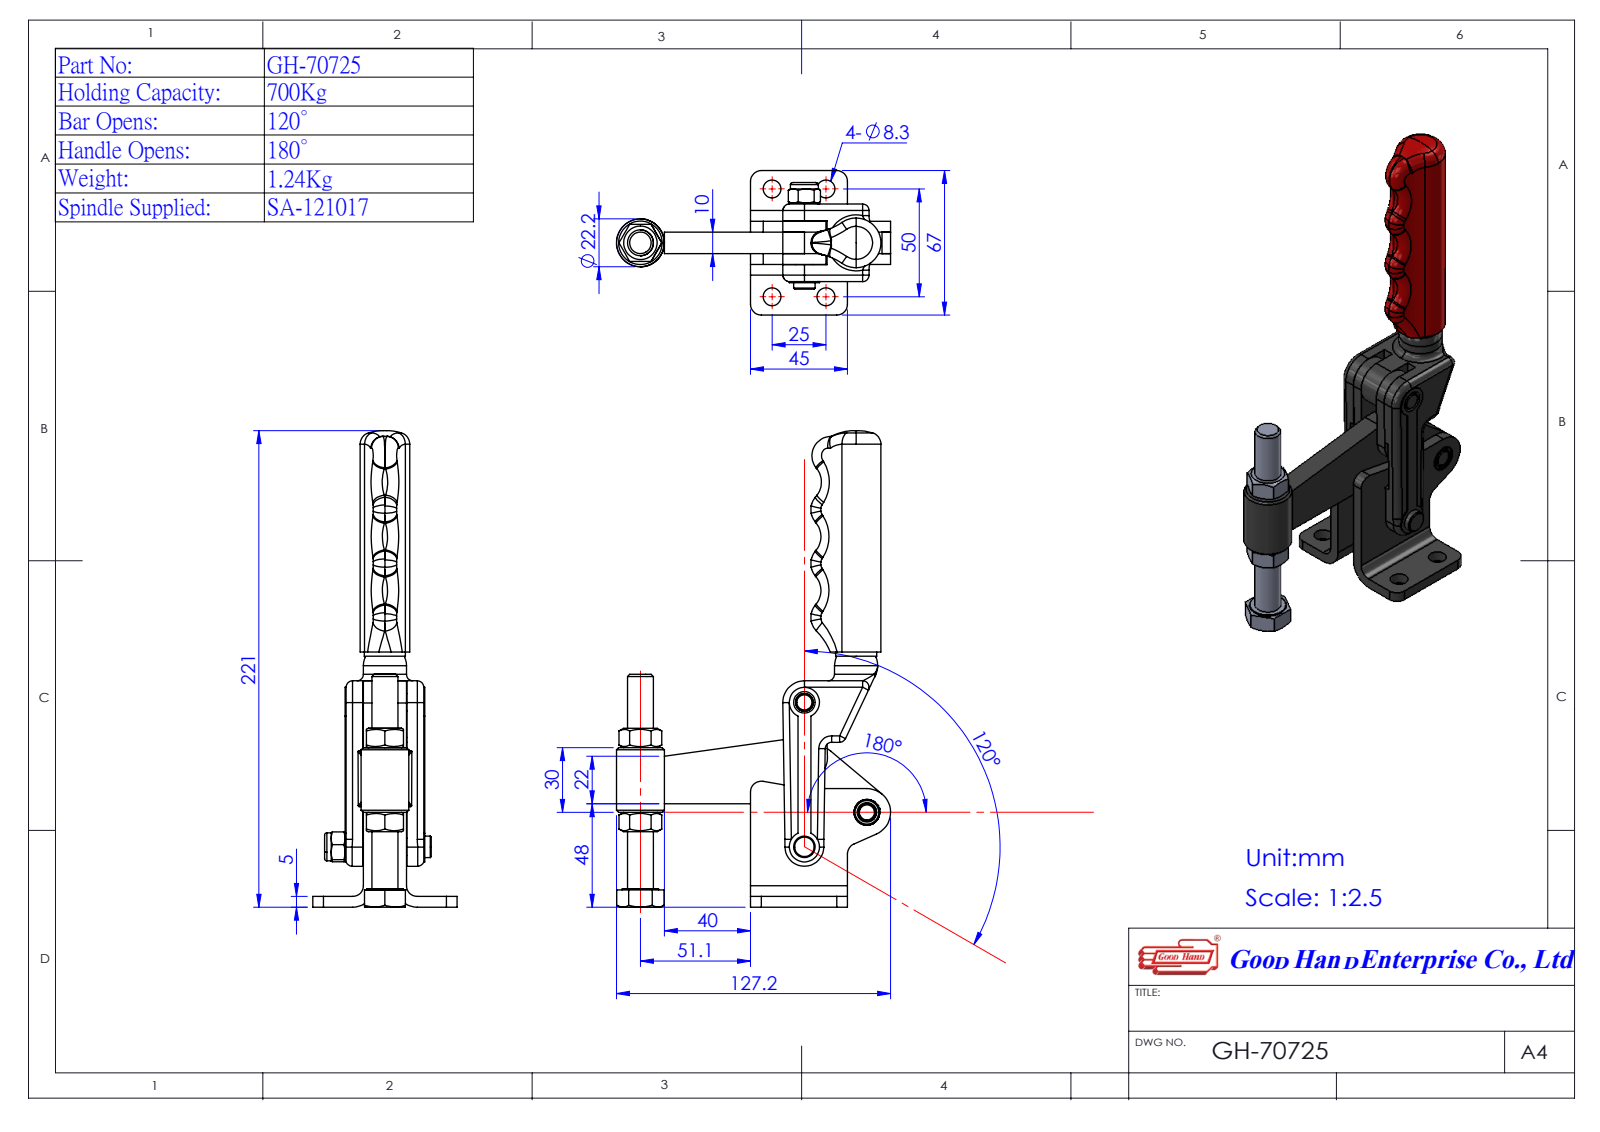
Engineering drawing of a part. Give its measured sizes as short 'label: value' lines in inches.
name: Group1^GH-70725(簡化)-1; Group5^GH-70725(簡化)-1; Group4^GH-70725(簡化)-1; GH-70725(簡化)-1 (+2 more)
written by: SolidWorks 2016 (AUTOMOTIVE_DESIGN)
unit: in
bodies: 6 solids, 362 faces (110 planar, 128 cylindrical, 124 other)
size: 8.702 × 5.008 × 2.638
volume: 12.06 in³; area: 100.7 in²
holes: 4× ⌀0.236, 4× ⌀0.327
bosses: 2× ⌀0.551, 1× ⌀0.874, 1× ⌀0.787, 1× ⌀0.75, 1× ⌀0.709, 1× ⌀0.472, 1× ⌀0.394
rounds: 13× R0.118, 7× R0.394, 7× R1.181, 6× R0.197, 5× R0.354, 3× R0.984, 2× R0.004, 2× R0.201
face distances: 0.197, 0.591, 0.394, 0.787, 0.203, 0.596, 0.793, 1.102, 0.02, 0.512
hole spacings: 0.984, 1.969, 2.201, 1.024, 1.304, 1.487, 1.615, 2.311
